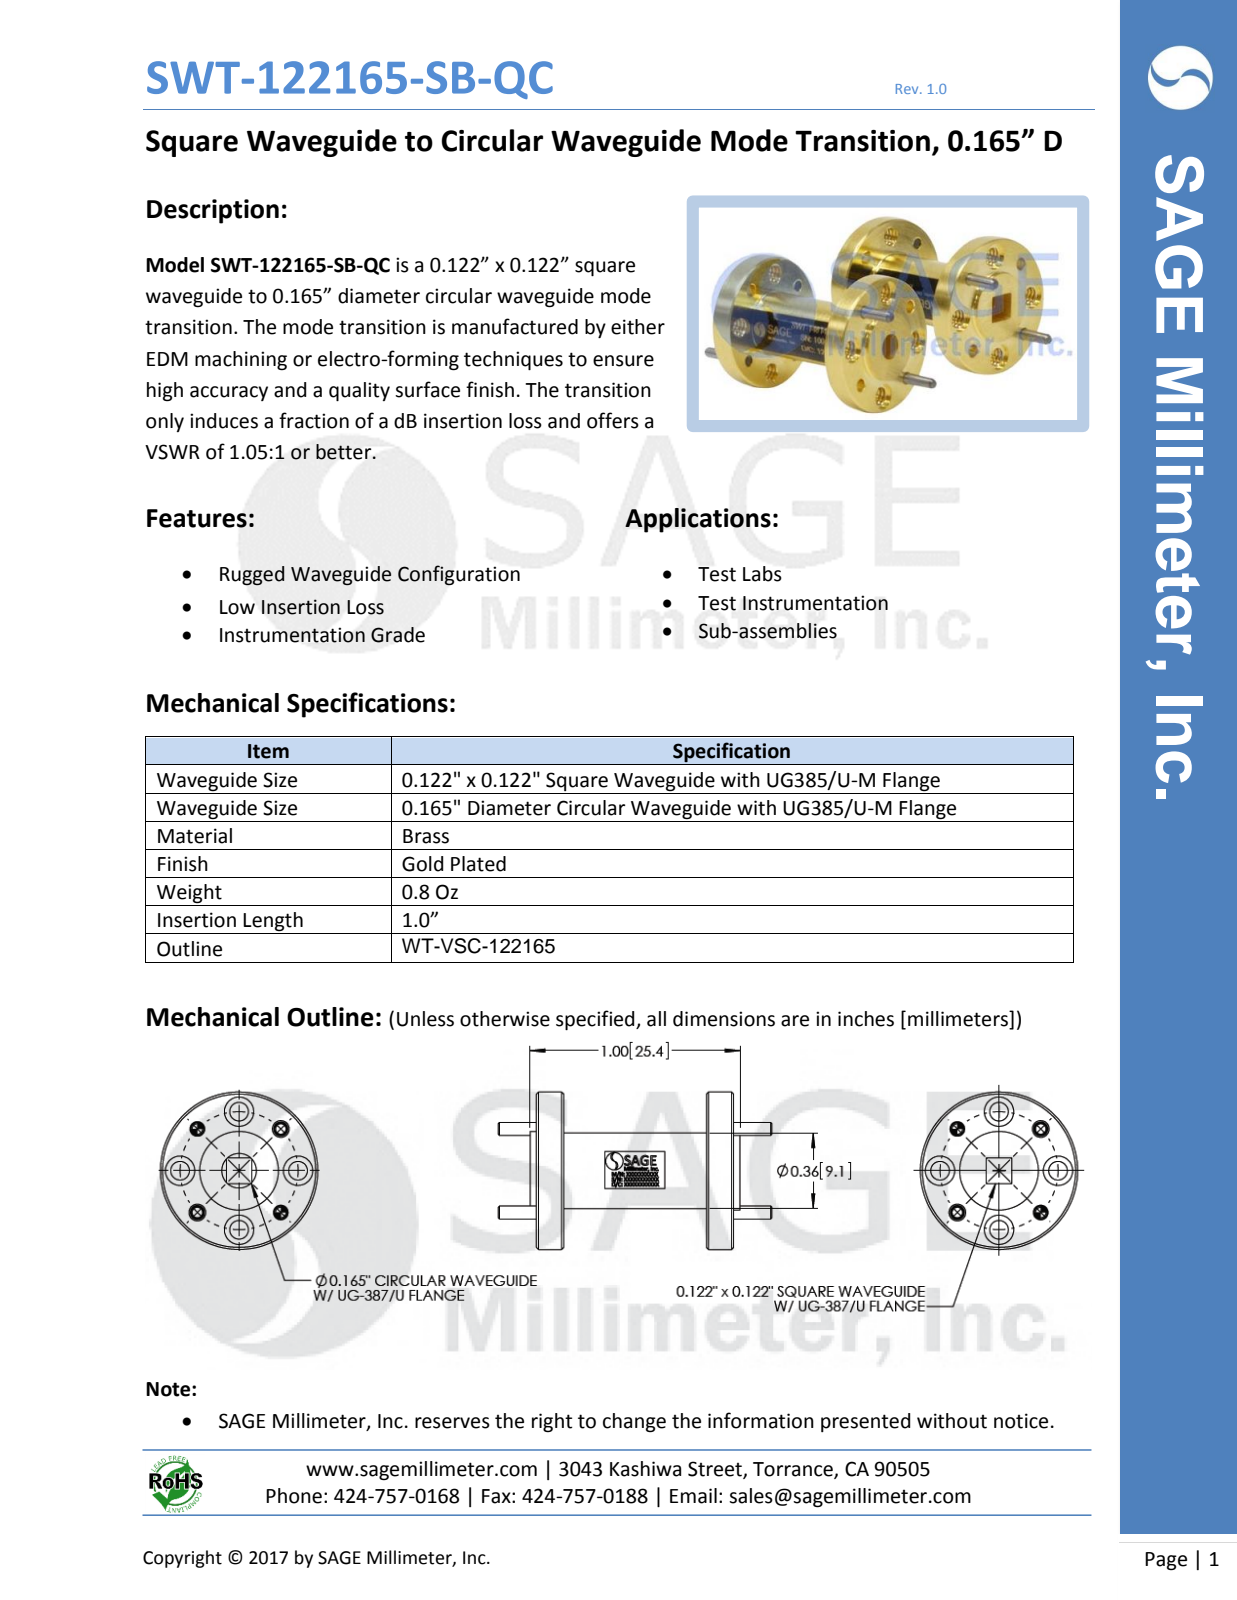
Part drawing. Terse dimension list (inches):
name: SWT-122165-SB-QC
written by: SolidWorks 2016 (CONFIG_CONTROL_DESIGN)
unit: in
bodies: 5 solids, 138 faces (24 planar, 66 cylindrical, 48 other)
size: 1.305 × 0.75 × 0.75
volume: 0.183 in³; area: 3.597 in²
holes: 4× ⌀0.06, 4× ⌀0.067, 4× ⌀0.089, 4× ⌀0.14
bosses: 4× ⌀0.063, 1× ⌀0.75, 1× ⌀0.375, 1× ⌀0.36
face distances: 0.68, 0.81, 0.13, 0.13, 0.81, 0.94, 0.03, 0.97, 0.84, 0.16
hole spacings: 0.215, 0.398, 0.519, 0.562, 0.52, 0.563
